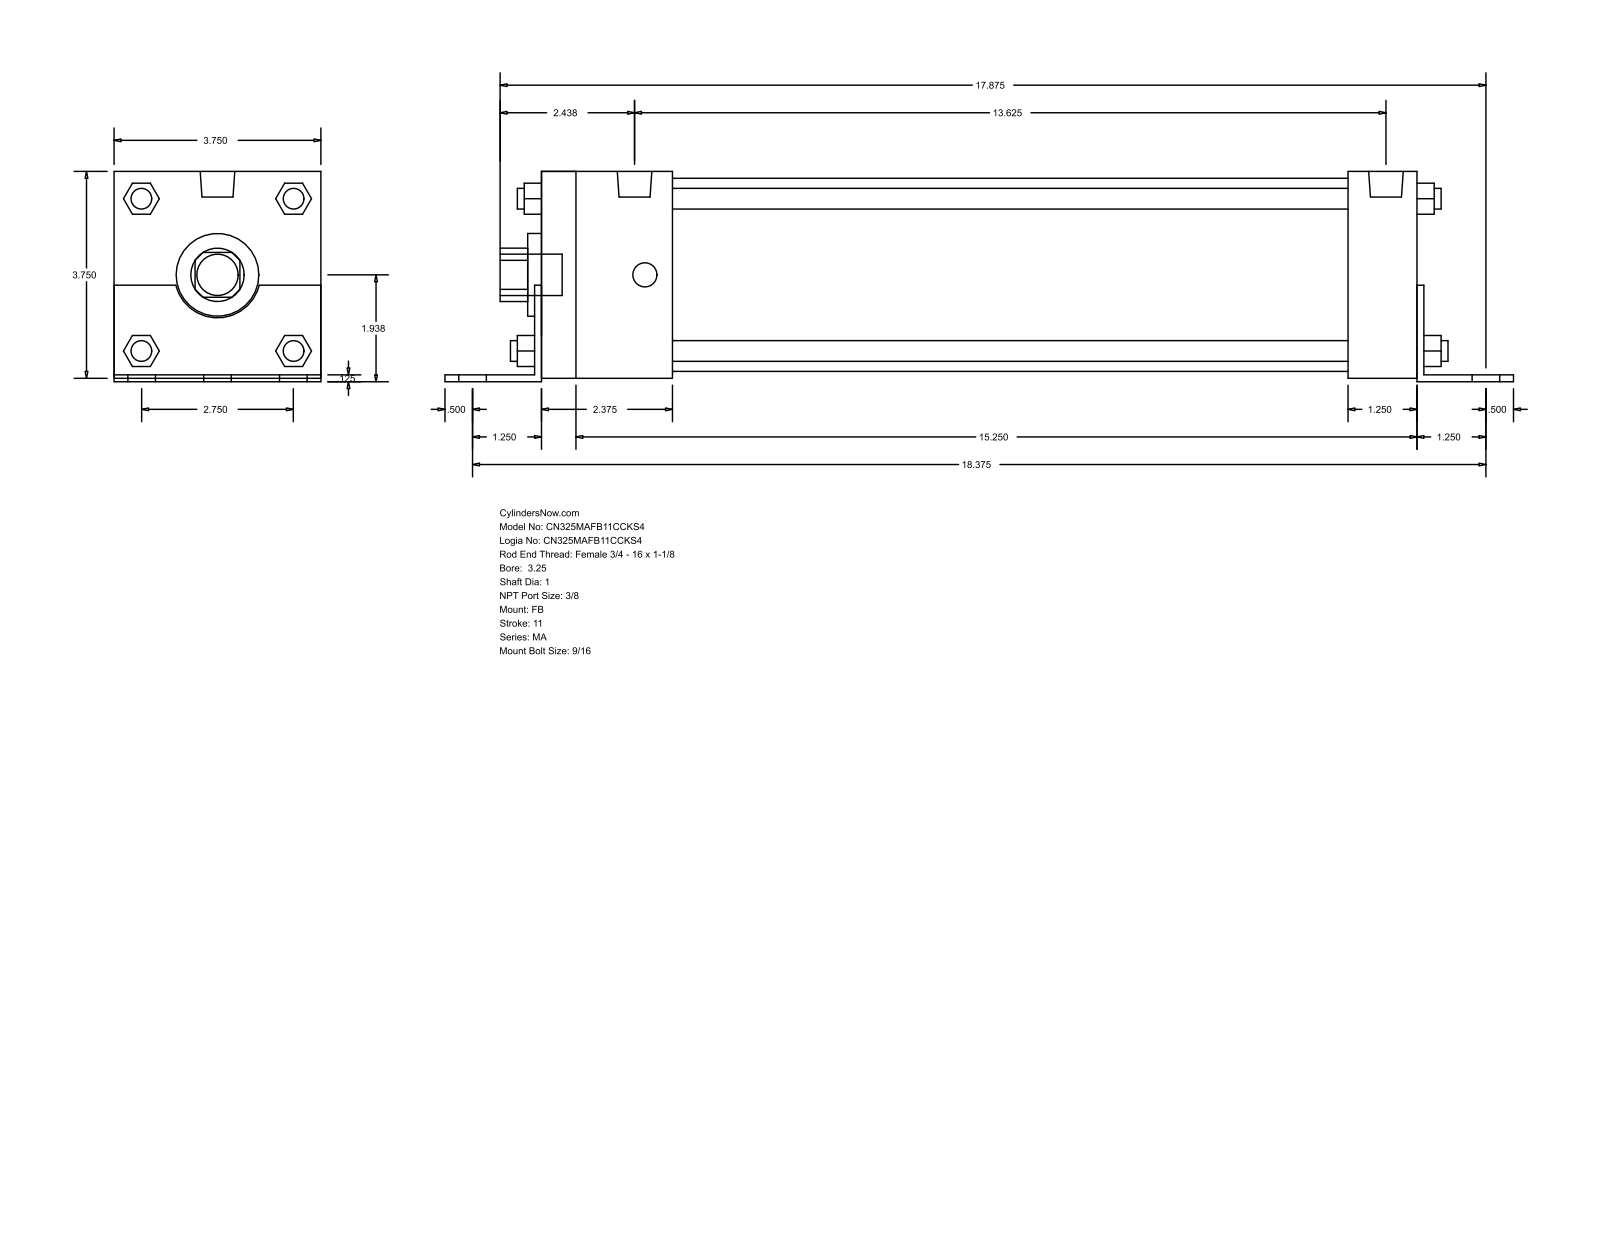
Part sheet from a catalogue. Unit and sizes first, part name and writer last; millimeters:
Units: millimetres
Overall size (bounding box): 492.12 × 96.84 × 95.25
Round holes (diameter × count): ⌀25.4 ×1, ⌀38.1 ×1, ⌀88.9 ×1
Round bosses / shafts (diameter × count): ⌀14.29 ×6, ⌀11.11 ×4, ⌀9.53 ×4, ⌀15.93 ×2, ⌀19.05 ×1
Partial cylindrical surfaces — rounded edges, fillets, slot ends (radius × count): R12.29 ×1, R19.81 ×1
Main face-to-face distances: 95.24, 3.17, 1.59, 96.83, 1.58, 93.66, 3.18, 403.22, 409.57, 406.4
Bodies: 0 solids, 140 faces (105 planar, 35 cylindrical, 0 other)
Part name (STEP PRODUCT): MA_FB__0325_1
STEP written by: GSSL Pune (CONFIG_CONTROL_DESIGN)
